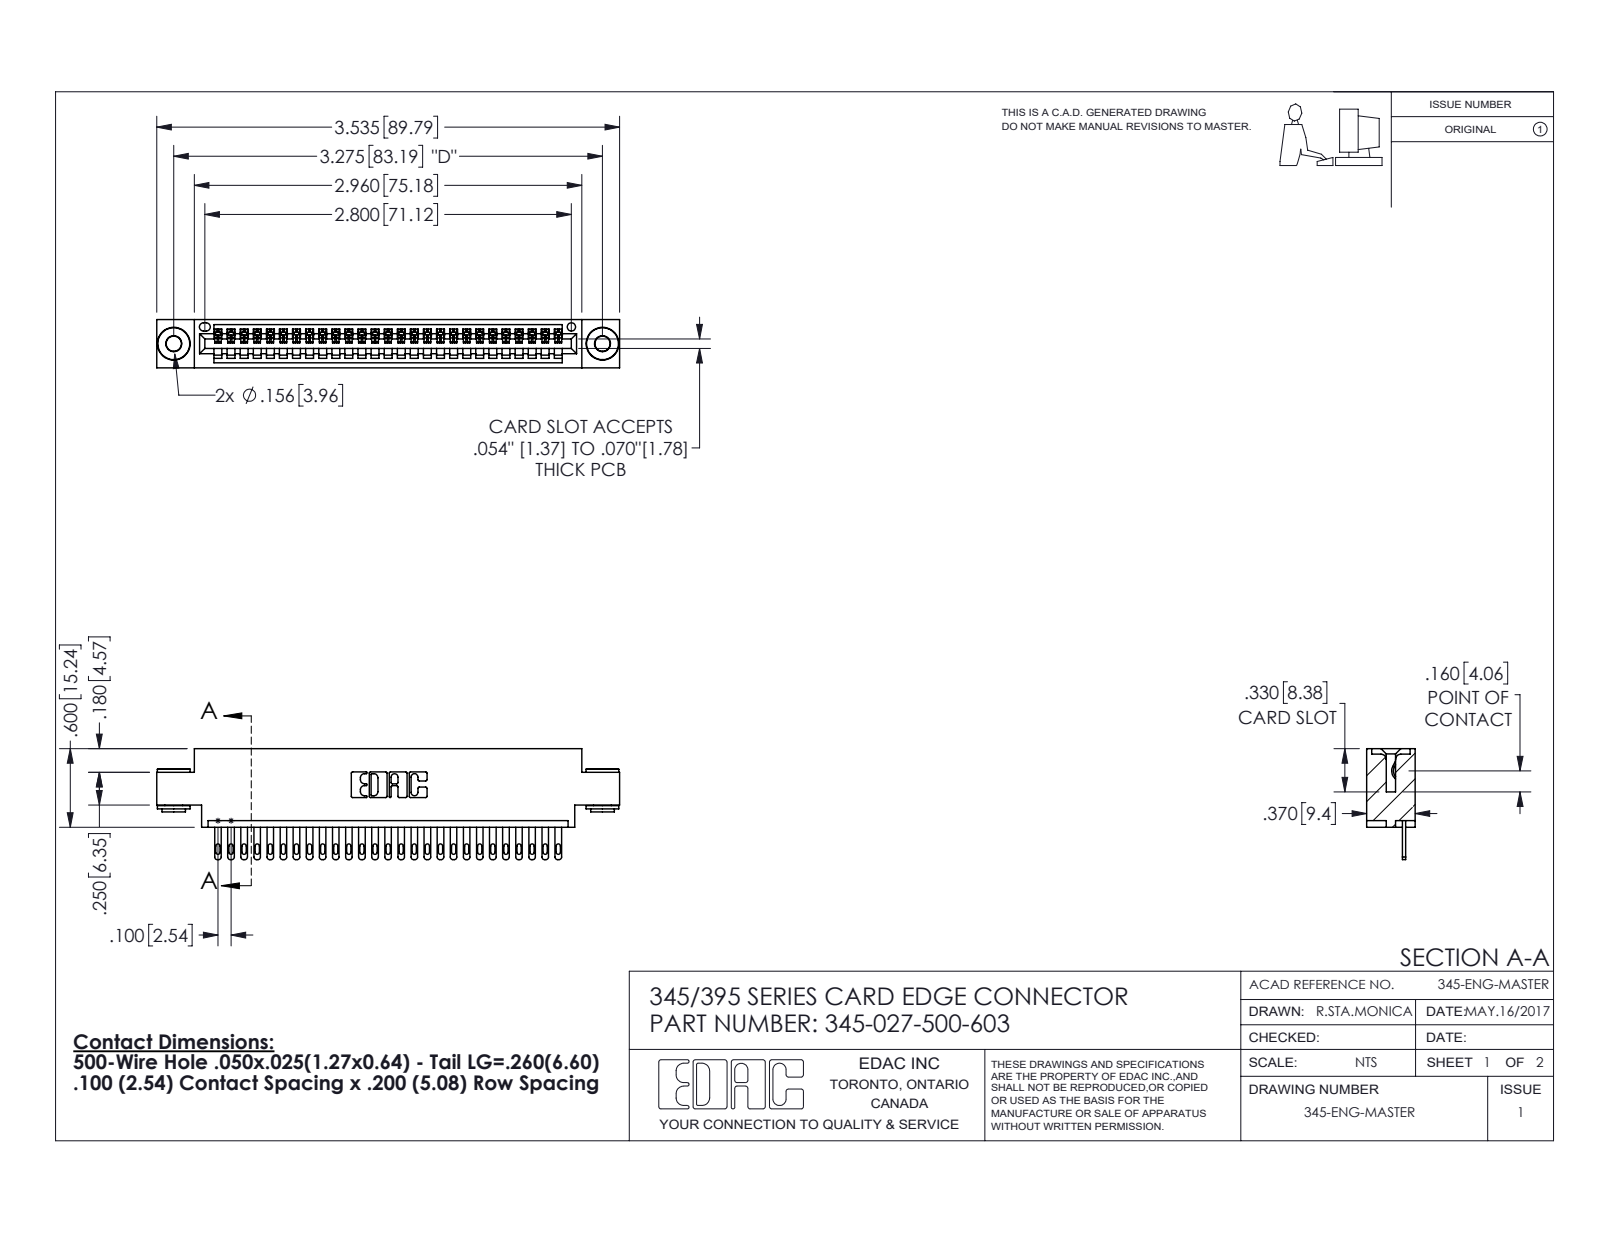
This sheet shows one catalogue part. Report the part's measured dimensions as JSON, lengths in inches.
{"part_name": "345 Part_0.170 Offset - 0.156 Dia-TH; 345-027-500-603; 345-250-002_345-250-002-102; 345-292-001_345-293-100", "step_written_by": "SolidWorks 2016 (CONFIG_CONTROL_DESIGN)", "units": "inches", "bodies": {"solids": 30, "faces": 1626, "planar": 1012, "cylindrical": 606, "other": 8}, "overall_size": [3.535, 0.847, 0.37], "volume_in3": 0.508, "surface_area_in2": 17.46, "round_holes": [[0.116, 2], [0.156, 2], [0.064, 1]], "round_bosses_or_shafts": [[0.25, 2], [0.18, 2], [0.136, 2]], "partial_cylinders_radius": [[0.006, 54], [0.016, 54], [0.02, 54], [0.01, 22], [0.007, 6], [0.031, 6], [0.026, 3], [0.031, 2]], "face_to_face_distances": [0.072, 0.298, 0.37, 0.2, 0.098, 0.272, 0.025, 0.225, 0.175, 0.1], "hole_center_spacings": [0.27, 3.04, 3.275]}
